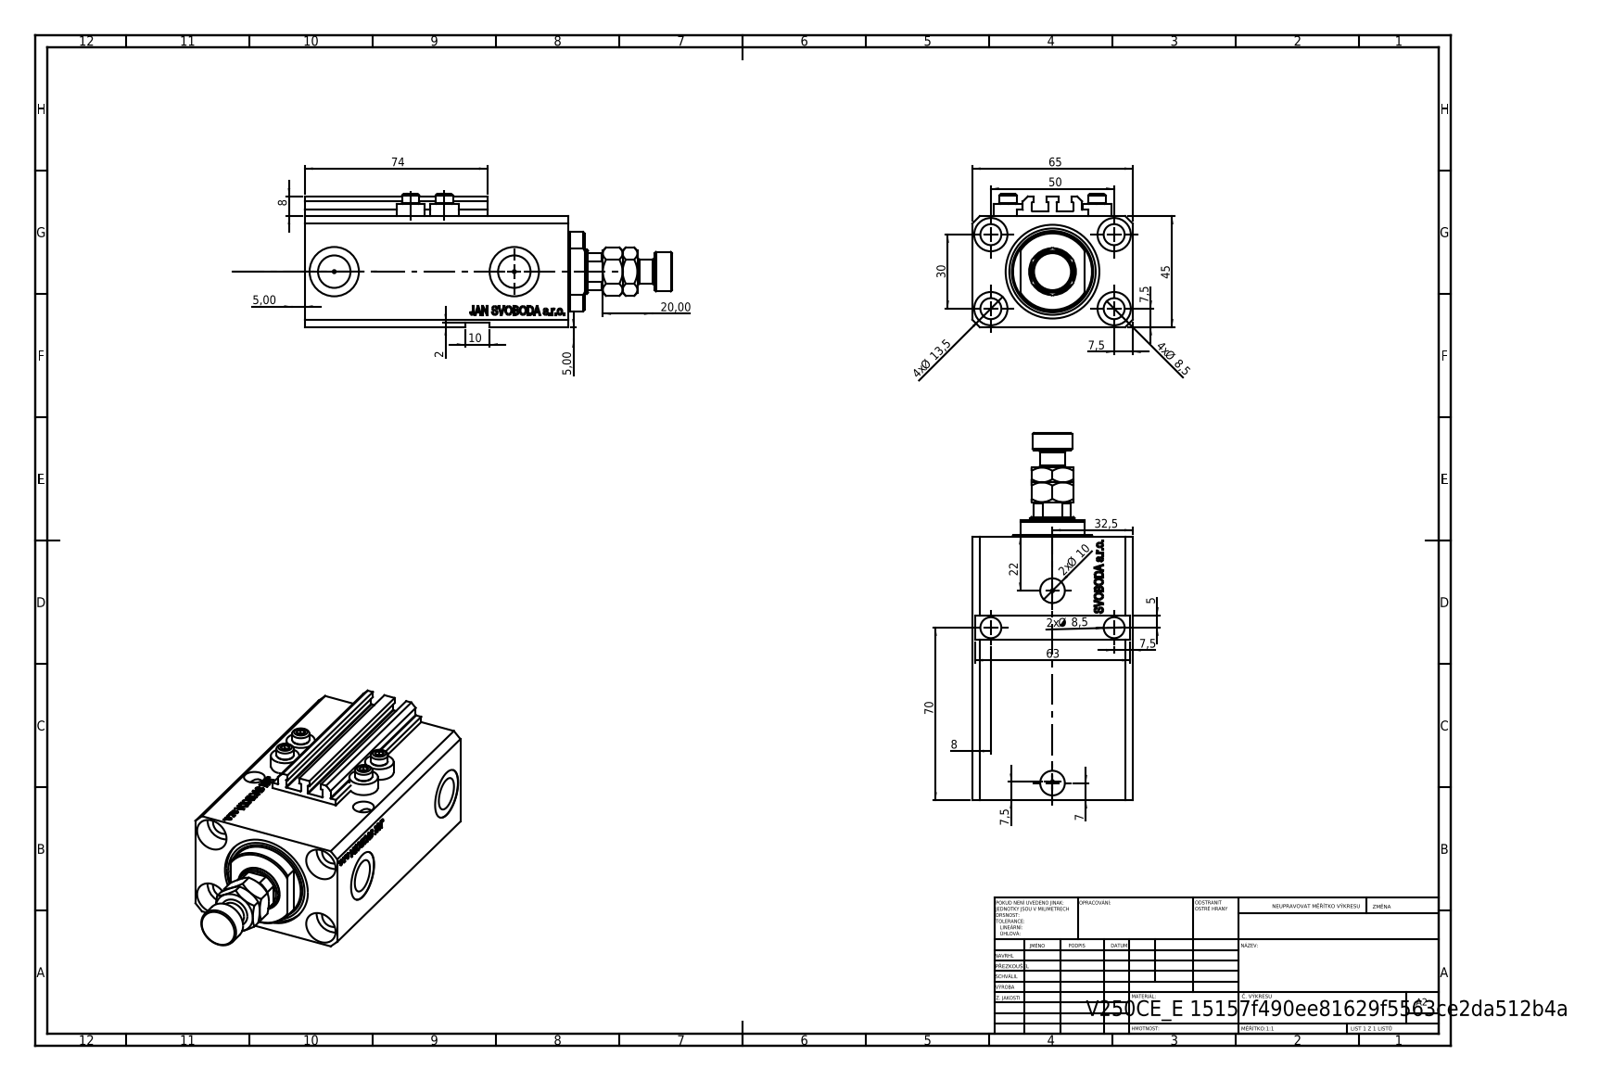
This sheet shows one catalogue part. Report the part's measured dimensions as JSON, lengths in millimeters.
{"part_name": "MFA; ALLEN BOLT V250CE; V250CE_C_VCP; V250CE_E_Body (+1 more)", "step_written_by": "SolidWorks 2019 (CONFIG_CONTROL_DESIGN)", "units": "millimeters", "bodies": {"solids": 9, "faces": 1135, "planar": 531, "cylindrical": 142, "other": 462}, "overall_size": [148.9, 65, 54], "volume_mm3": 278677, "surface_area_mm2": 81137, "round_holes": [[8.5, 7], [1.25, 4], [4, 4], [13.5, 4], [10, 2], [13.16, 2], [20, 2], [18, 1], [25, 1], [38, 1]], "round_bosses_or_shafts": [[11.6, 4], [7, 4], [16, 1], [10, 1]], "partial_cylinders_radius": [[0.2, 10], [8.5, 1], [16, 1]], "face_to_face_distances": [45, 65, 81.9, 2, 47, 6.9, 107, 25.1, 24, 2.5], "hole_center_spacings": [29.15, 50, 13.6, 15.12, 27.89, 30, 33.62, 36]}
